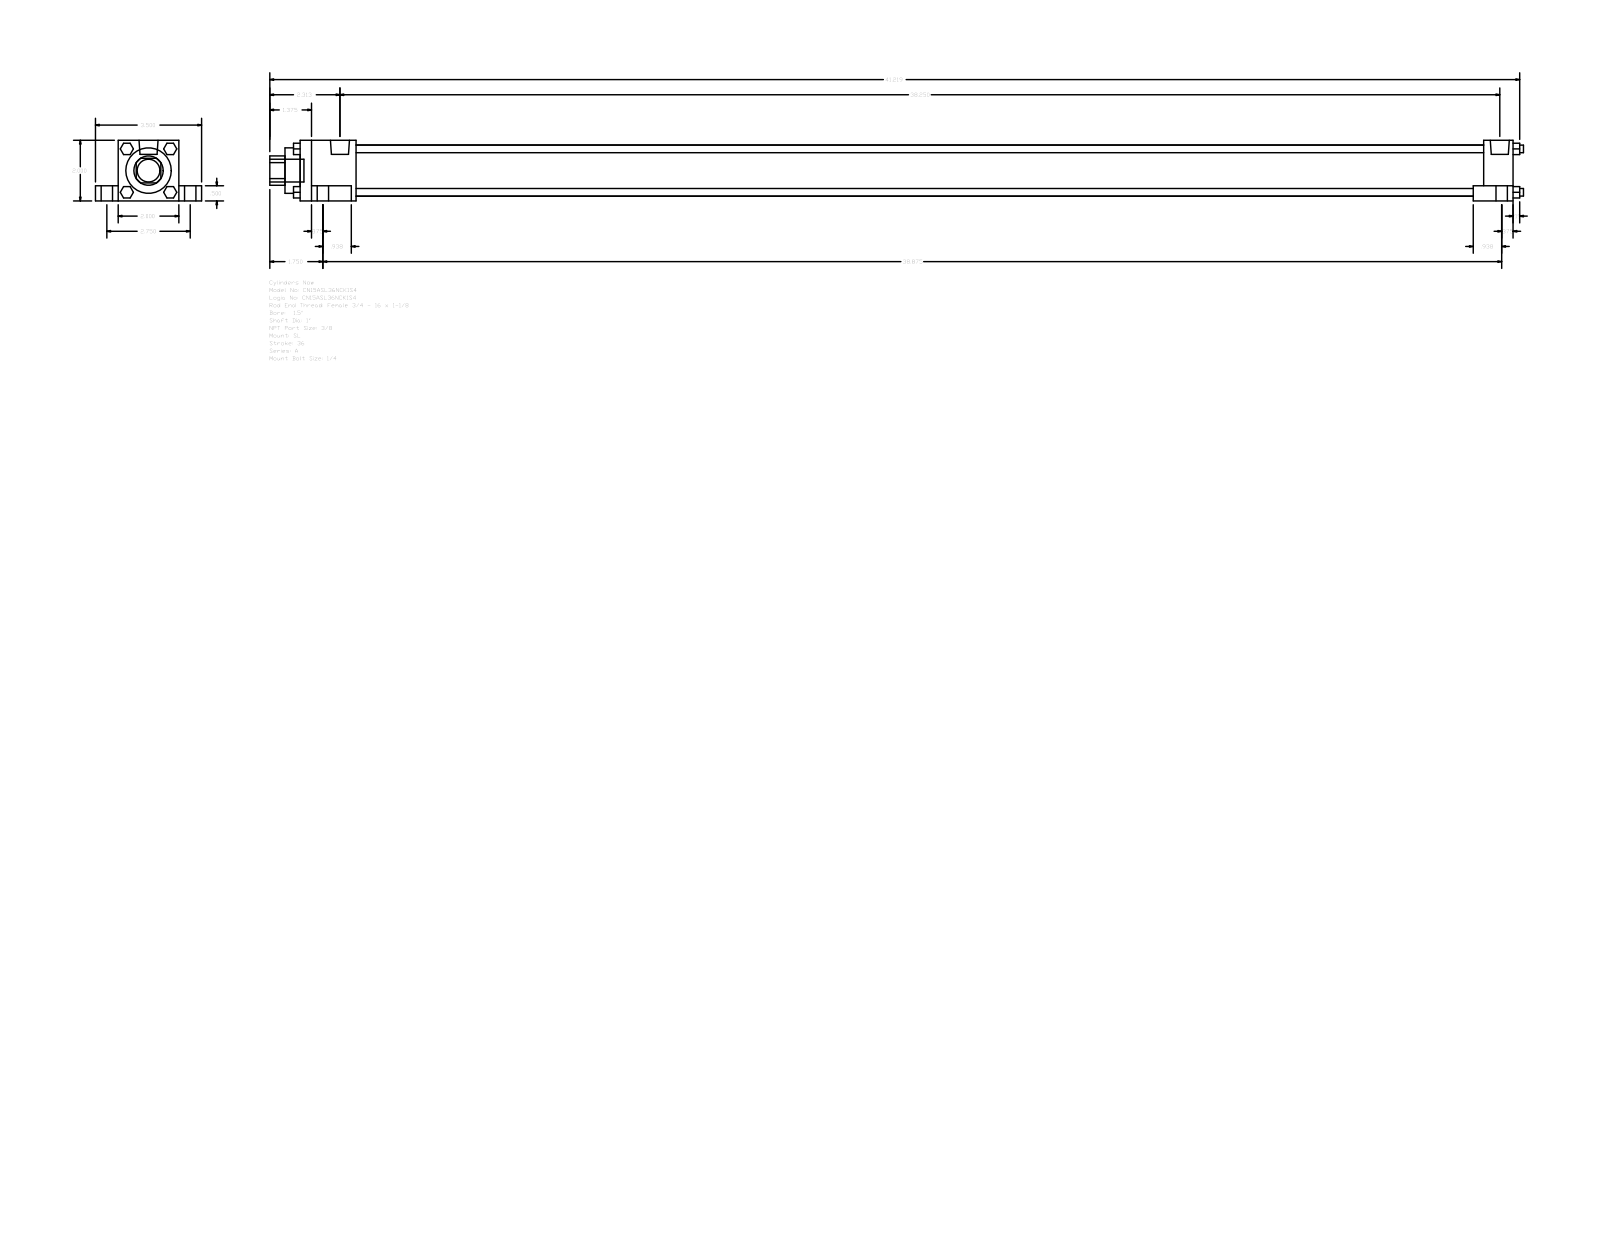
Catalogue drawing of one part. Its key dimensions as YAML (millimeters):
part_name: "A_SL__0150_1"
step_written_by: "GSSL Pune (CONFIG_CONTROL_DESIGN)"
units: millimeters
bodies: {solids: 0, faces: 148, planar: 112, cylindrical: 36, other: 0}
overall_size: [1050.13, 88.9, 50.8]
round_holes:
  - {diameter: 25.4, count: 1}
  - {diameter: 38.1, count: 1}
  - {diameter: 42.93, count: 1}
round_bosses_or_shafts:
  - {diameter: 15.88, count: 4}
  - {diameter: 9.53, count: 4}
  - {diameter: 6.35, count: 4}
  - {diameter: 5.56, count: 4}
  - {diameter: 15.93, count: 2}
  - {diameter: 19.05, count: 1}
partial_cylinders:
  - {radius: 12.29, count: 1}
face_to_face_distances: [50.8, 12.7, 38.1, 19.05, 69.85, 9.52, 1016, 33.34, 991.39, 24.61]
